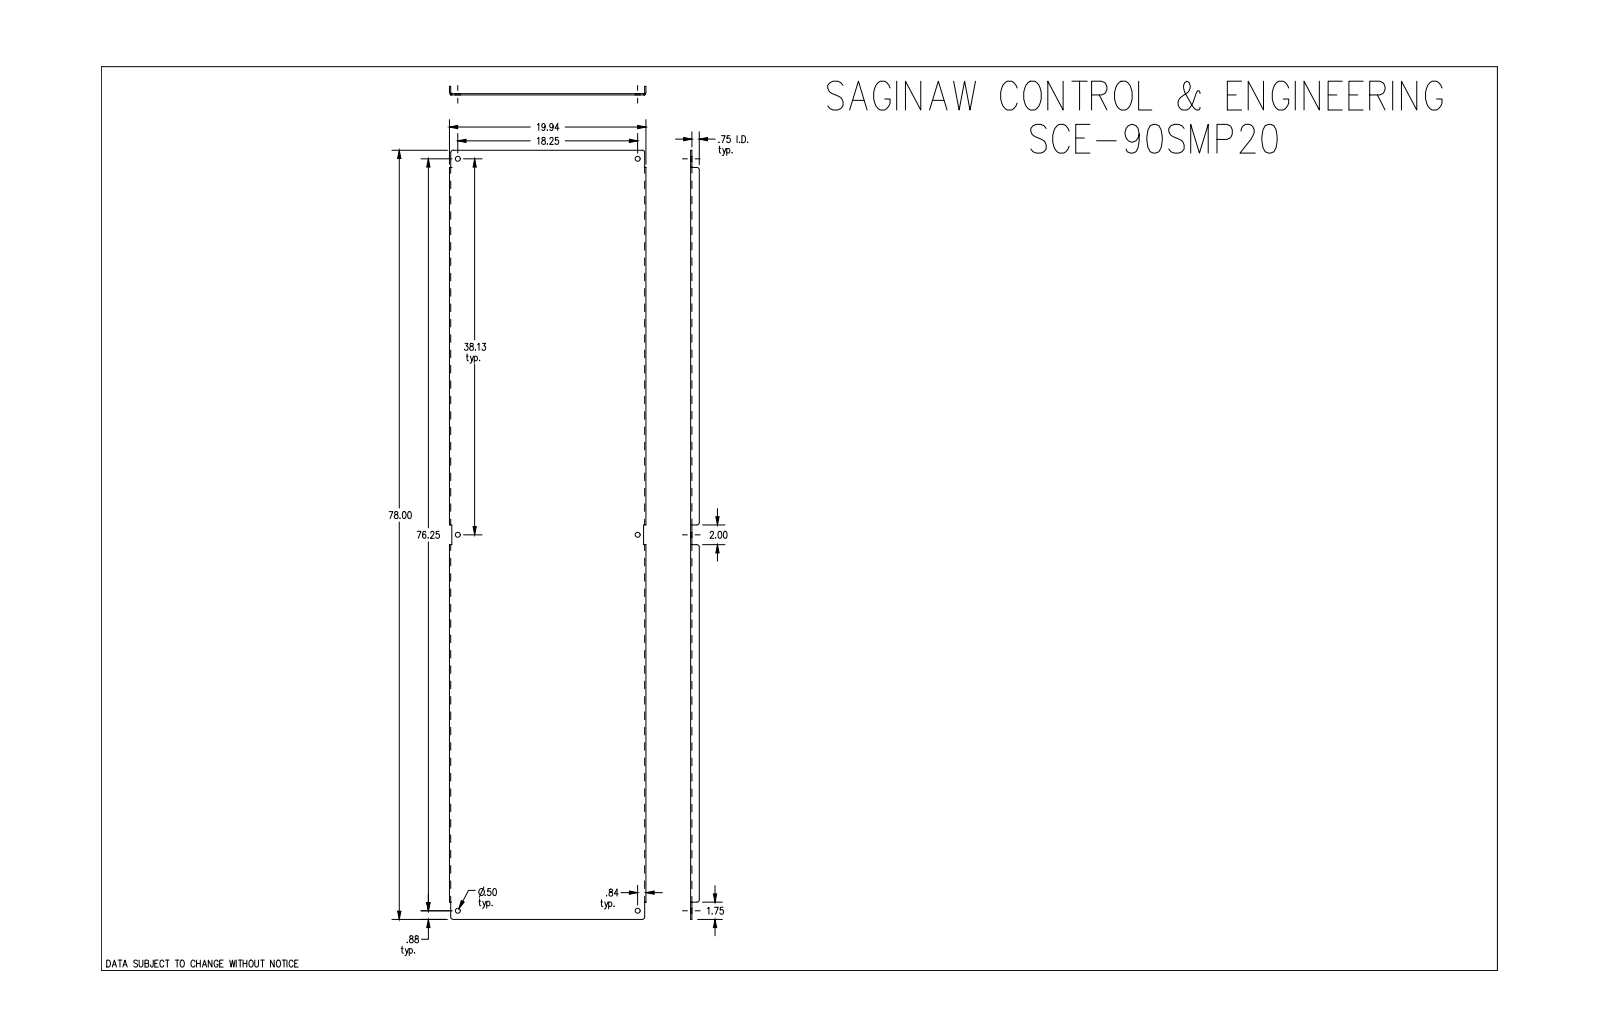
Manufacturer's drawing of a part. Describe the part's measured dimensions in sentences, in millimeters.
The part is named "SCE-90SMP20". Its 3-D file was written by "SolidWorks 2019 (CONFIG_CONTROL_DESIGN)". It is 1 solid with 68 faces: 30 planar, 26 cylindrical and 12 other. Overall it measures 1981.2 by 506.4 by 22.2 millimeters. Its volume is 3 379 000 cubic millimeters and its surface area 2 146 000 square millimeters. Round holes: 6 of diameter 12.7. Partial cylindrical surfaces (rounded edges, fillets, slot ends): 8 of radius 6.4, 2 of radius 2.8, 2 of radius 6. The main face-to-face distances are 3.2, 3.2, 503.3, 500, 506.4, 19.1, 22.2, 1981.2, 6, 500.4. The hole center spacings are 968.4, 1073.6, 463.6, 1936.8, 1991.5.
